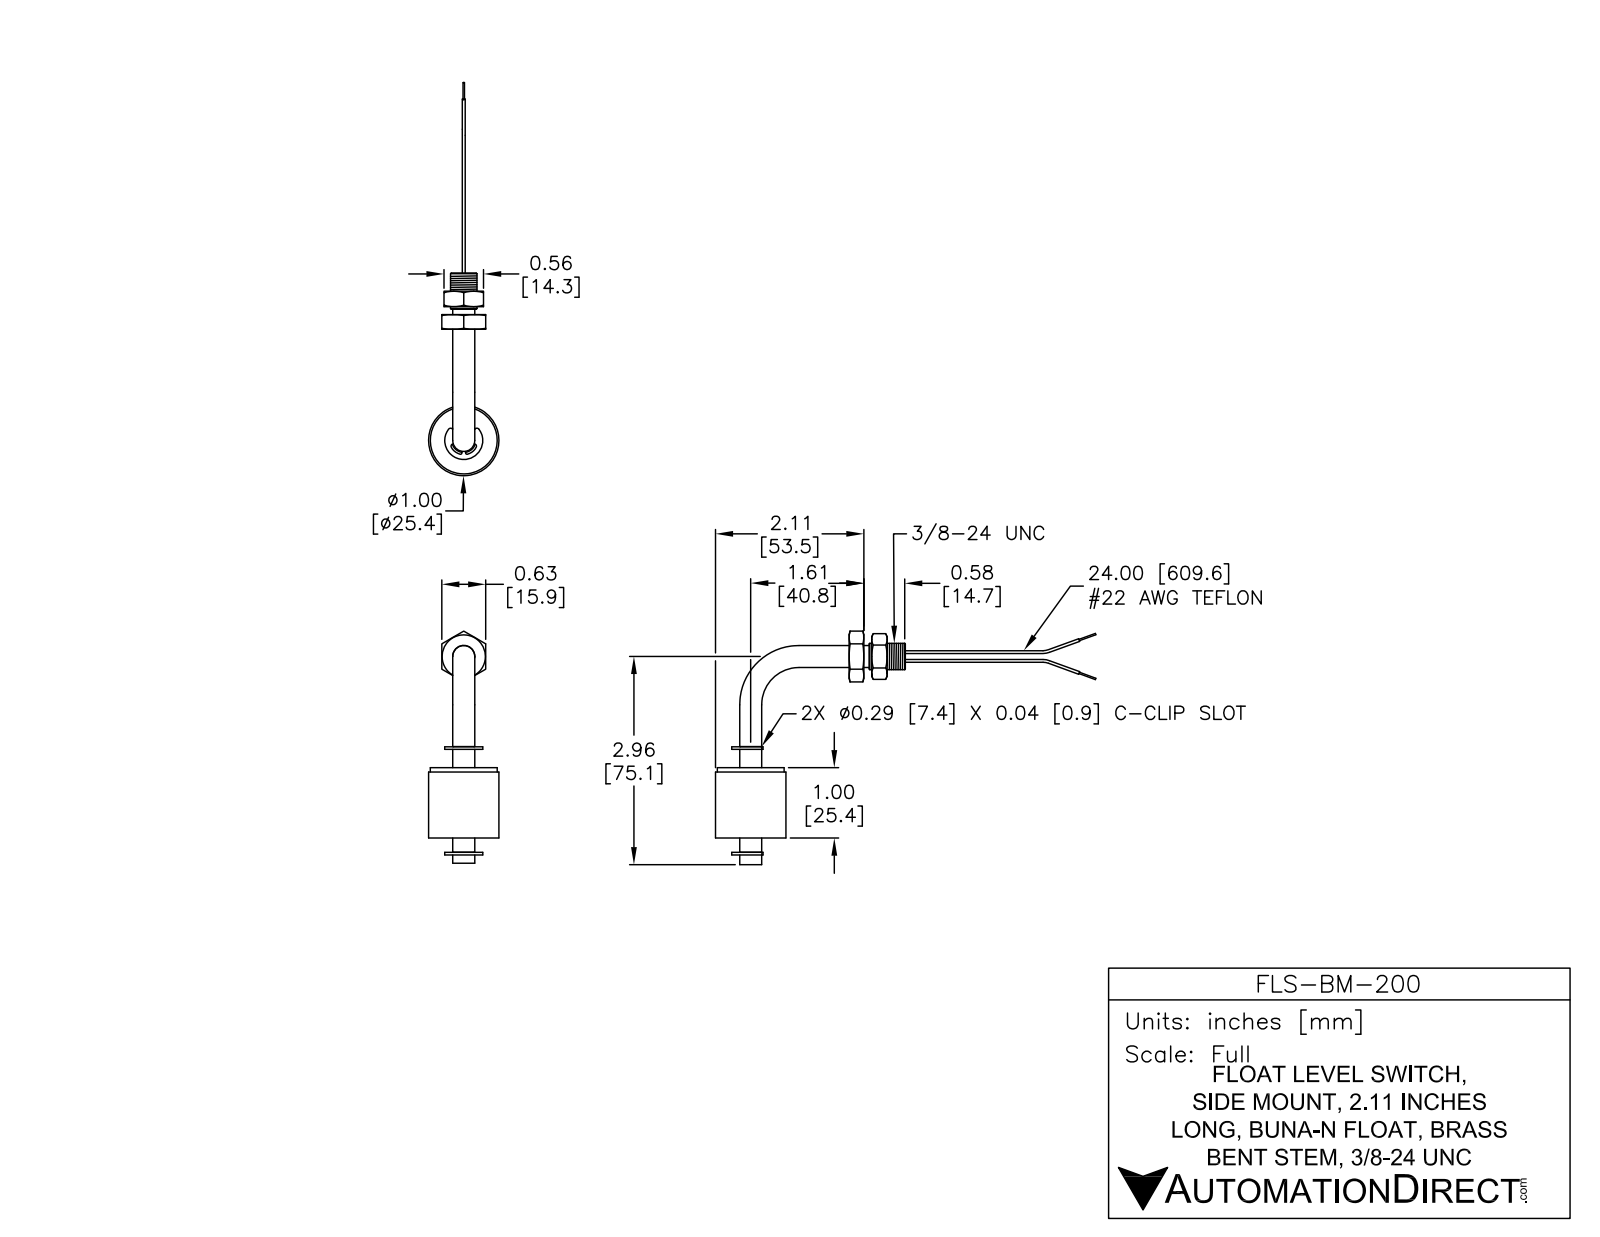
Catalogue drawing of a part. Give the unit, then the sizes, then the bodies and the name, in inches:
Units: inches
Overall size (bounding box): 5.289 × 3.324 × 1.01
Round holes (diameter × count): ⌀0.344 ×1
Round bosses / shafts (diameter × count): ⌀0.04 ×4, ⌀0.25 ×3, ⌀0.313 ×2, ⌀0.02 ×2, ⌀1 ×1, ⌀0.375 ×1
Partial cylindrical surfaces — rounded edges, fillets, slot ends (radius × count): R0.008 ×4, R0.02 ×4, R0.03 ×4, R0.038 ×4, R0.025 ×2, R0.126 ×2, R0.202 ×2, R0.27 ×2
Main face-to-face distances: 1, 0.213, 0.46, 0.625, 0.037, 1.657, 0.248, 0.673, 0.462, 0.675
Volume: 1.185 in³ · Surface area: 13.9 in²
Bodies: 8 solids, 140 faces (50 planar, 80 cylindrical, 10 other)
Part name (STEP PRODUCT): FLS-BM-200
STEP written by: SolidWorks 2013 (AUTOMOTIVE_DESIGN)
